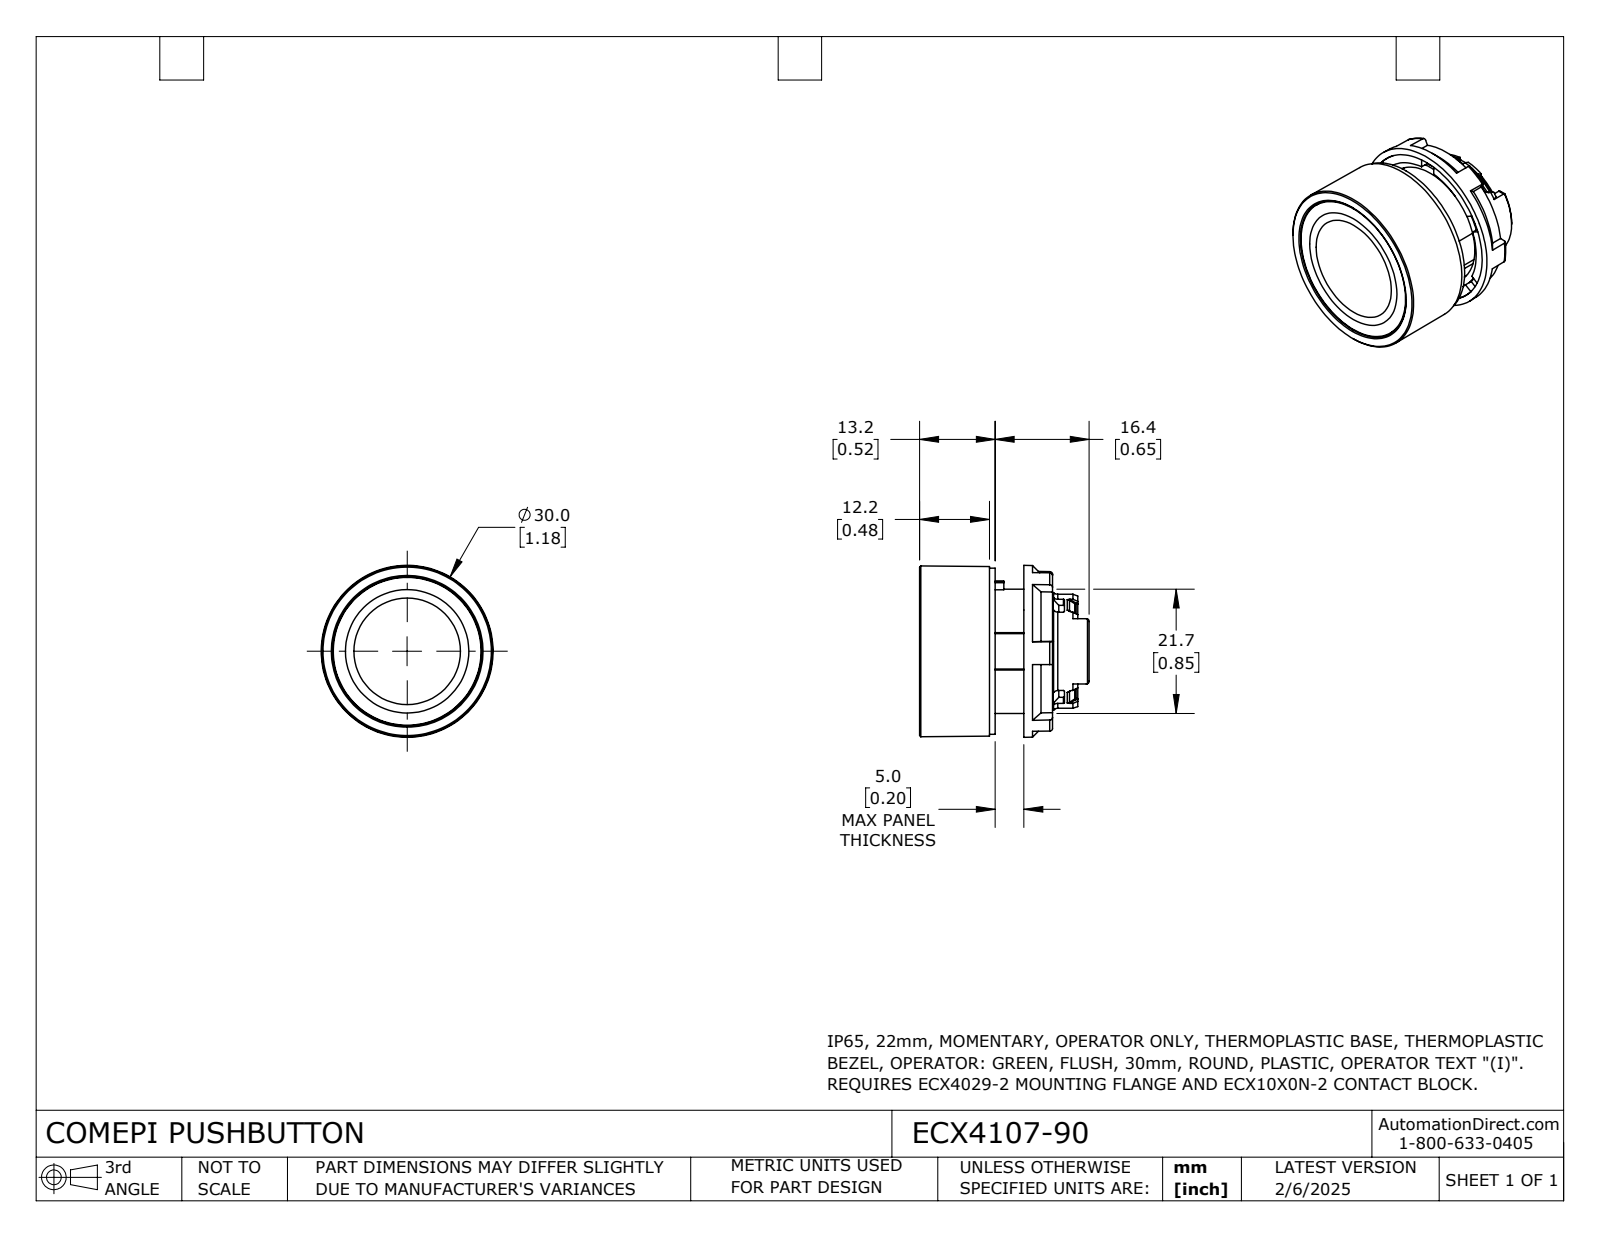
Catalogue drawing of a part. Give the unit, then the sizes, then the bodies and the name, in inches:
Units: inches
Overall size (bounding box): 1.181 × 1.181 × 1.165
Round holes (diameter × count): ⌀0.531 ×1, ⌀0.713 ×1, ⌀0.866 ×1
Round bosses / shafts (diameter × count): ⌀1.142 ×1, ⌀1.016 ×1, ⌀0.965 ×1, ⌀0.854 ×1, ⌀0.807 ×1, ⌀0.787 ×1, ⌀0.748 ×1, ⌀0.728 ×1
Partial cylindrical surfaces — rounded edges, fillets, slot ends (radius × count): R0.008 ×24, R0.02 ×8, R0.01 ×2, R0.293 ×1, R0.344 ×1, R0.348 ×1, R0.366 ×1
Main face-to-face distances: 0.409, 0.039, 0.433, 0.472, 0.236, 0.394, 0.197, 0.449, 0.512, 0.217
Volume: 0.472 in³ · Surface area: 16.55 in²
Bodies: 3 solids, 398 faces (134 planar, 111 cylindrical, 153 other)
Part name (STEP PRODUCT): ECX4107-90
STEP written by: SolidWorks 2024 (CONFIG_CONTROL_DESIGN)
